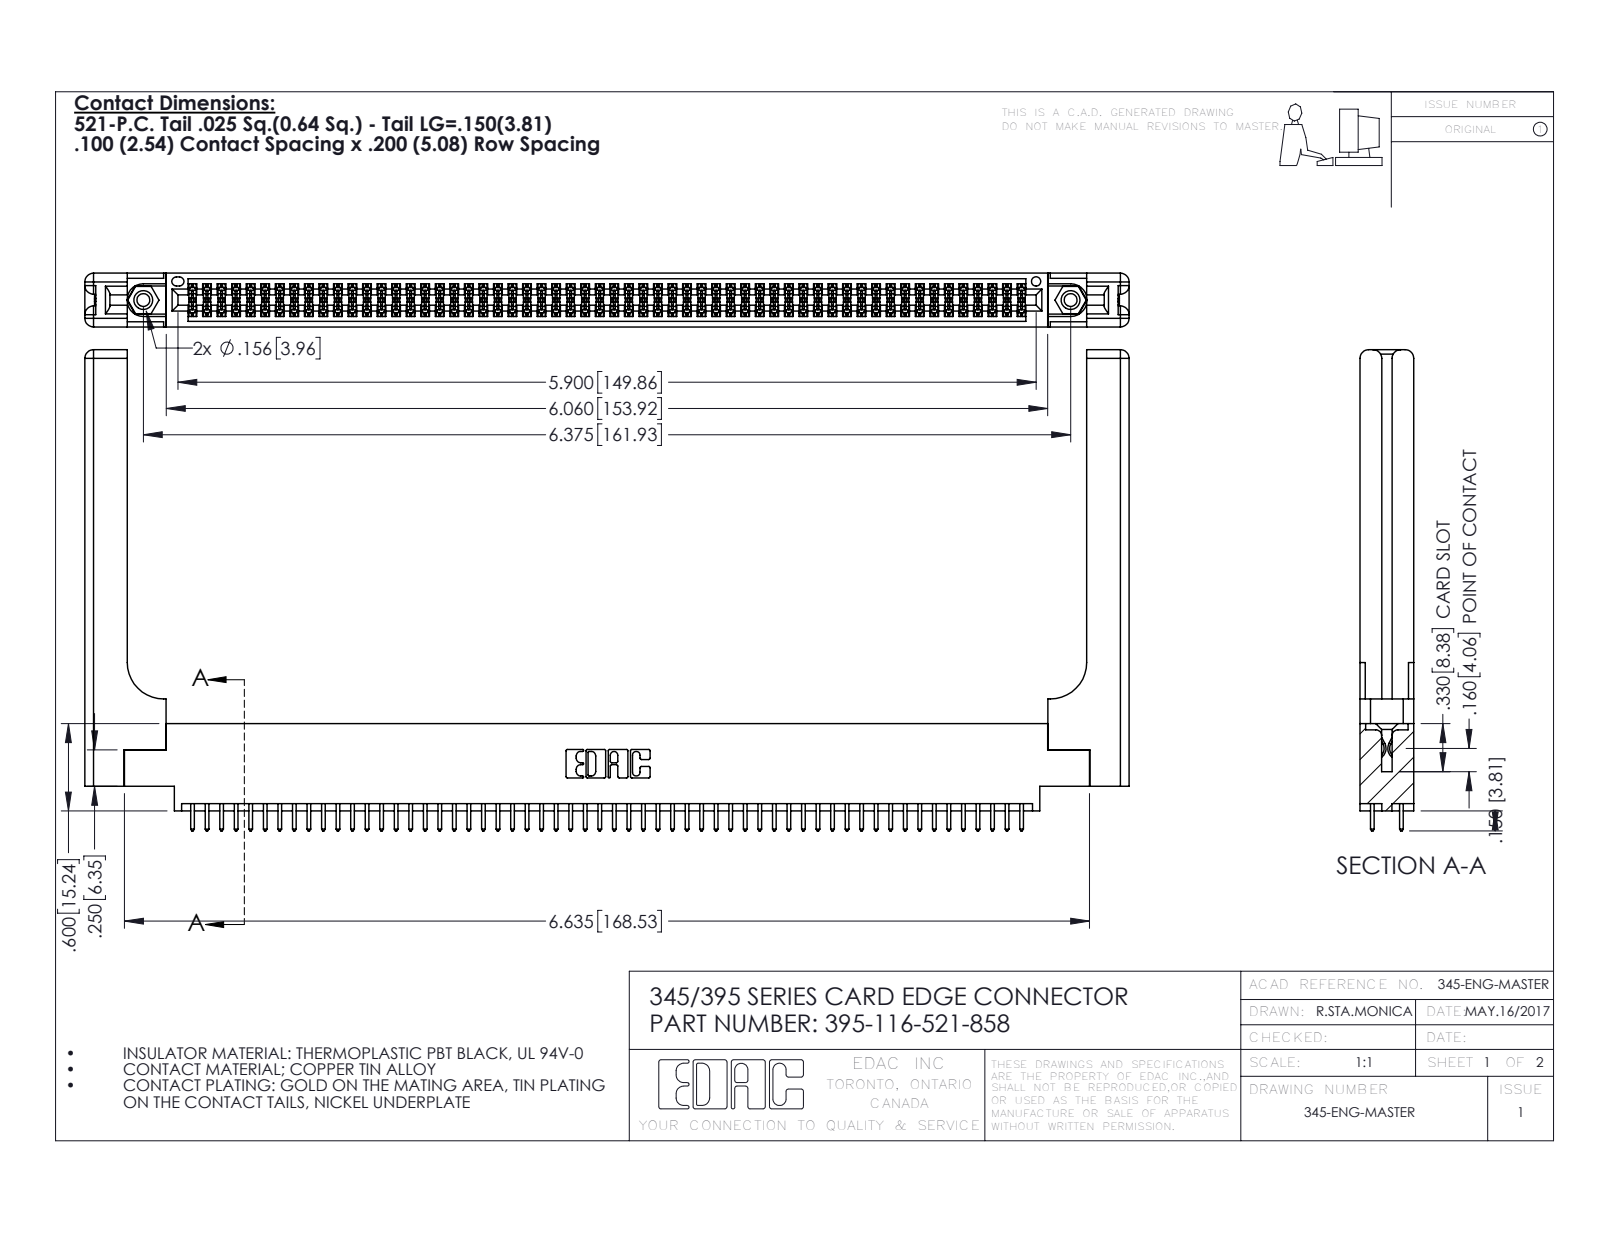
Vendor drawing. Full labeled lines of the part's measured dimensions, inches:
Part name (STEP PRODUCT): 345-220-058_345-220-058; 345 Part_0.170 Offset - 0.156 Dia-TH; 345-292-001_345-293-121; 345-250-001_345-250-001-102 (+1 more)
STEP written by: SolidWorks 2016 (CONFIG_CONTROL_DESIGN)
Units: inches
Bodies: 121 solids, 6186 faces (4060 planar, 2066 cylindrical, 60 other)
Overall size (bounding box): 7.179 × 3.307 × 0.37
Volume: 1.597 in³ · Surface area: 48.62 in²
Round holes (diameter × count): ⌀0.089 ×2, ⌀0.125 ×2, ⌀0.156 ×2, ⌀0.064 ×1
Round bosses / shafts (diameter × count): ⌀0.155 ×2
Partial cylindrical surfaces — rounded edges, fillets, slot ends (radius × count): R0.006 ×174, R0.01 ×116, R0.01 ×22, R0.06 ×16, R0.007 ×6, R0.031 ×6, R0.026 ×3, R0.014 ×2
Main face-to-face distances: 0.072, 0.298, 0.37, 0.098, 0.272, 0.025, 0.2, 0.225, 0.175, 0.148
Hole centre spacings: 0.27, 6.139, 6.375
